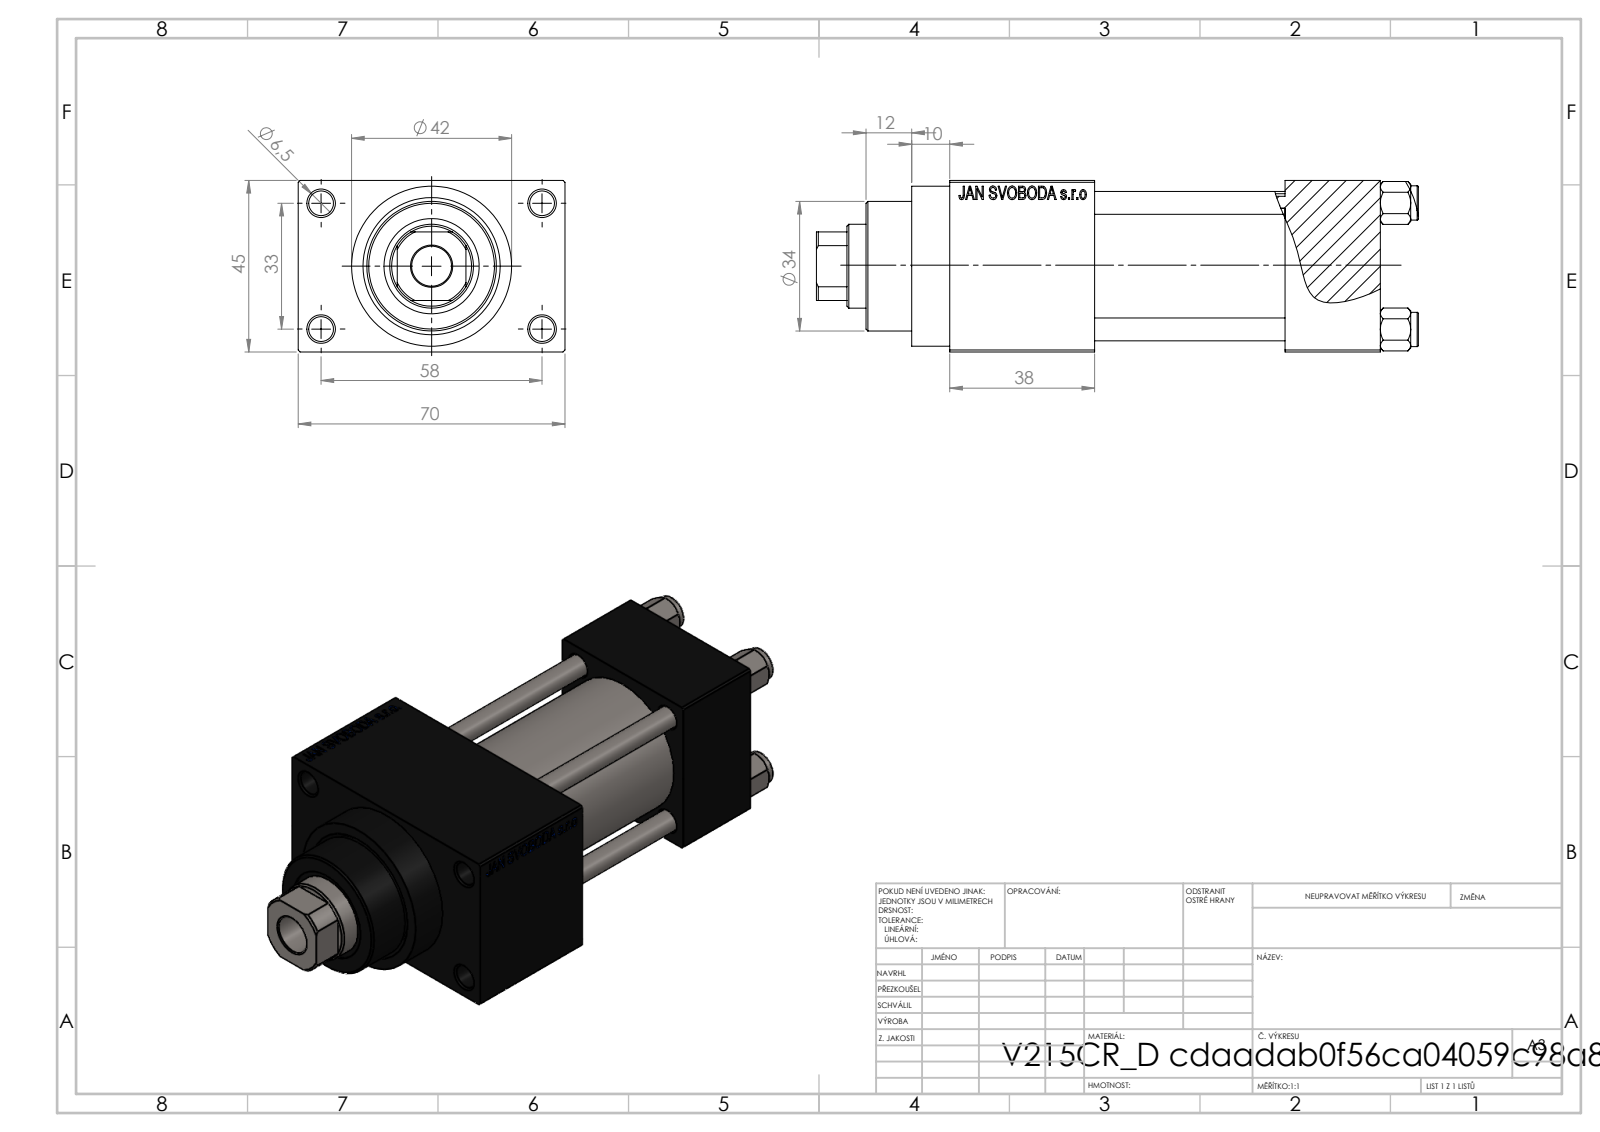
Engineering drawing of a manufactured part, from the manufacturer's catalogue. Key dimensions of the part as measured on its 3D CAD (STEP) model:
Part name (STEP PRODUCT): V215CR_VCP_D; V215CR_D_TYCINKA; V215_VC_A; NUT_M5_D (+1 more)
STEP written by: SolidWorks 2019 (CONFIG_CONTROL_DESIGN)
Units: millimetres
Bodies: 11 solids, 1105 faces (496 planar, 89 cylindrical, 520 other)
Overall size (bounding box): 158 × 70 × 45
Volume: 244 506 mm³ · Surface area: 79 366 mm²
Round holes (diameter × count): ⌀6 ×4, ⌀6.5 ×4, ⌀7 ×2, ⌀13.16 ×2, ⌀20 ×2, ⌀10.5 ×1, ⌀22 ×1, ⌀24 ×1, ⌀25 ×1, ⌀32 ×1, ⌀33 ×1
Round bosses / shafts (diameter × count): ⌀9 ×4, ⌀42 ×1, ⌀38 ×1, ⌀34 ×1
Partial cylindrical surfaces — rounded edges, fillets, slot ends (radius × count): R10.5 ×1
Main face-to-face distances: 45, 25, 12.5, 57.5, 50, 75, 88, 70, 38, 113
Hole centre spacings: 12.4, 23.48, 33.2, 33.37, 35.35, 45.6, 56.35, 33
